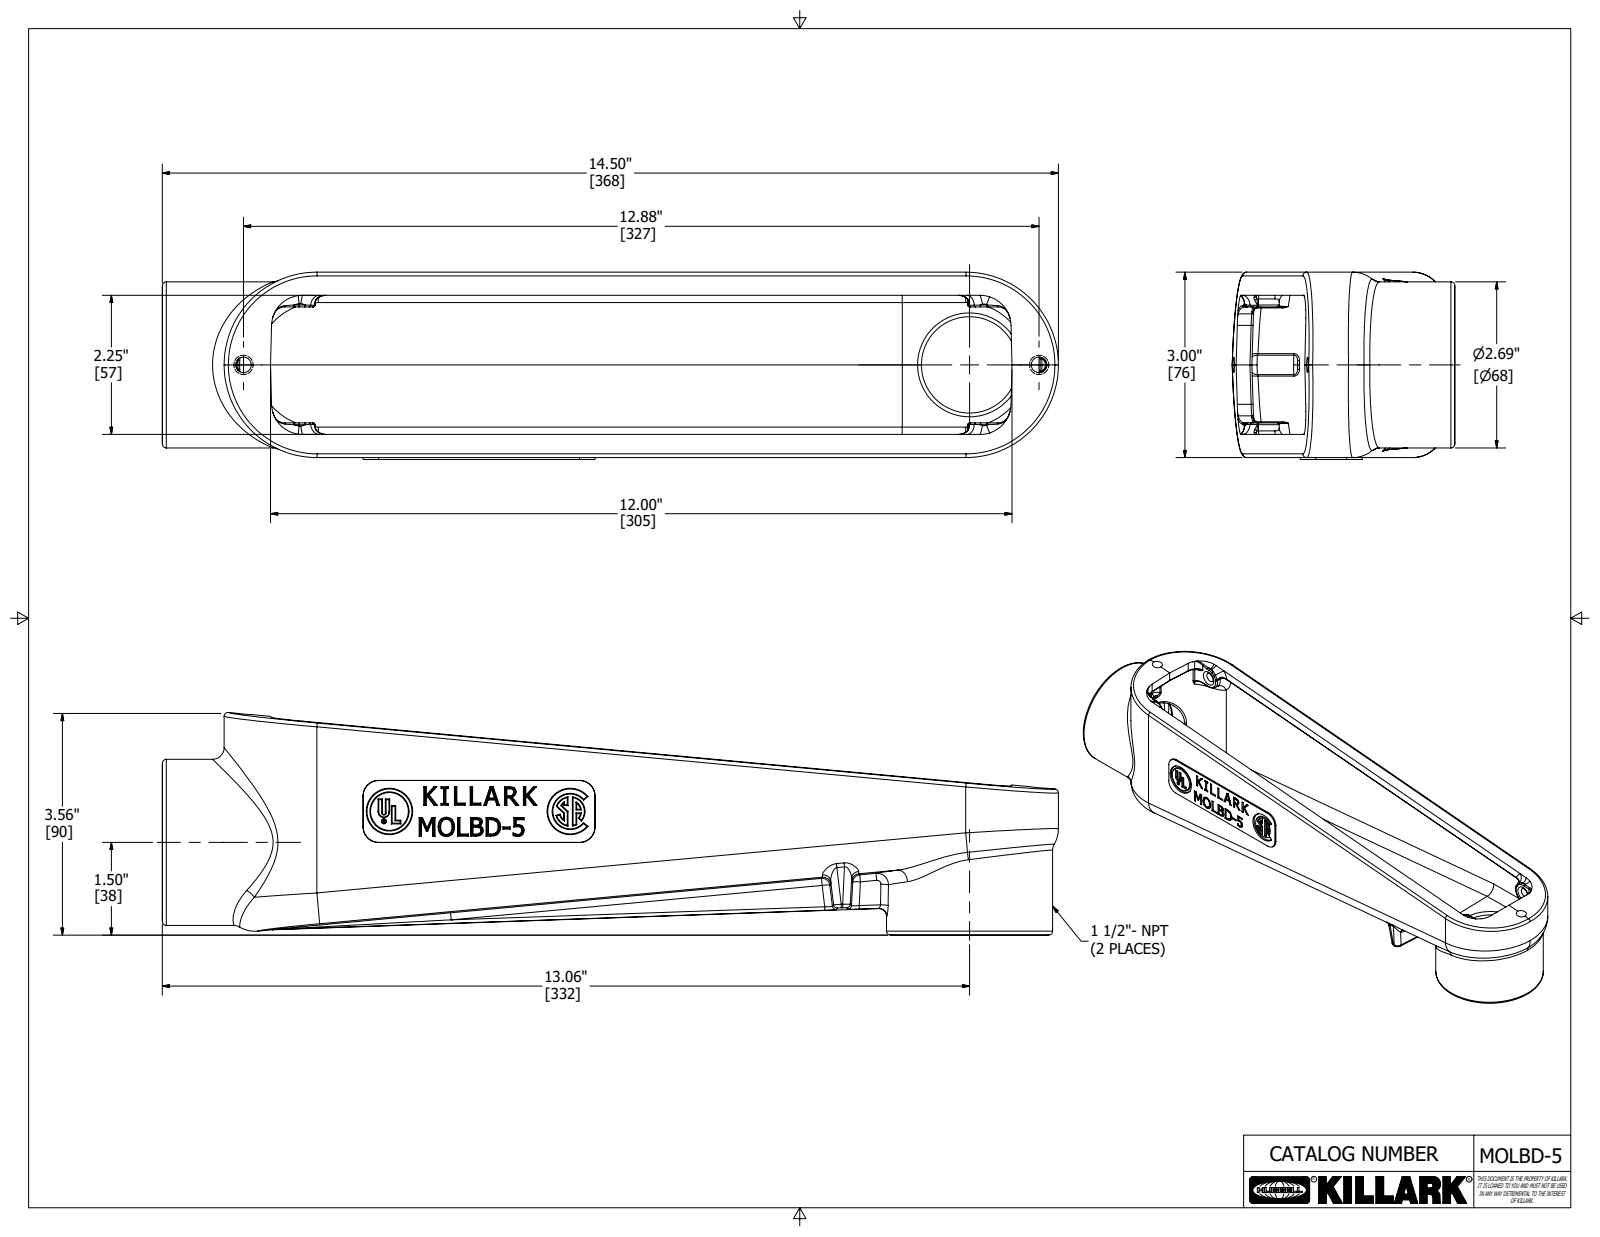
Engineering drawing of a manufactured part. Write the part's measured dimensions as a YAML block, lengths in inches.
part_name: "21016-2"
step_written_by: "Autodesk Inventor 2020 (AUTOMOTIVE_DESIGN)"
units: inches
bodies: {solids: 1, faces: 752, planar: 286, cylindrical: 89, other: 377}
overall_size: [14.5, 3.602, 3.031]
volume: 33.02
surface_area: 238.7
round_holes:
  - {diameter: 0.252, count: 2}
  - {diameter: 1.558, count: 2}
  - {diameter: 1.906, count: 2}
  - {diameter: 0.083, count: 1}
round_bosses_or_shafts:
  - {diameter: 2.688, count: 2}
  - {diameter: 0.07, count: 1}
partial_cylinders:
  - {radius: 0.125, count: 18}
  - {radius: 0.031, count: 12}
  - {radius: 0.062, count: 12}
  - {radius: 0.031, count: 8}
  - {radius: 0.187, count: 6}
  - {radius: 0.5, count: 6}
  - {radius: 0.25, count: 4}
  - {radius: 0.171, count: 2}
face_to_face_distances: [0.25, 2.75, 2.5, 3, 2.375, 0.375, 2.625, 0.125, 0.281, 0.031]
hole_center_spacings: [1.125, 11.75, 12.875]
